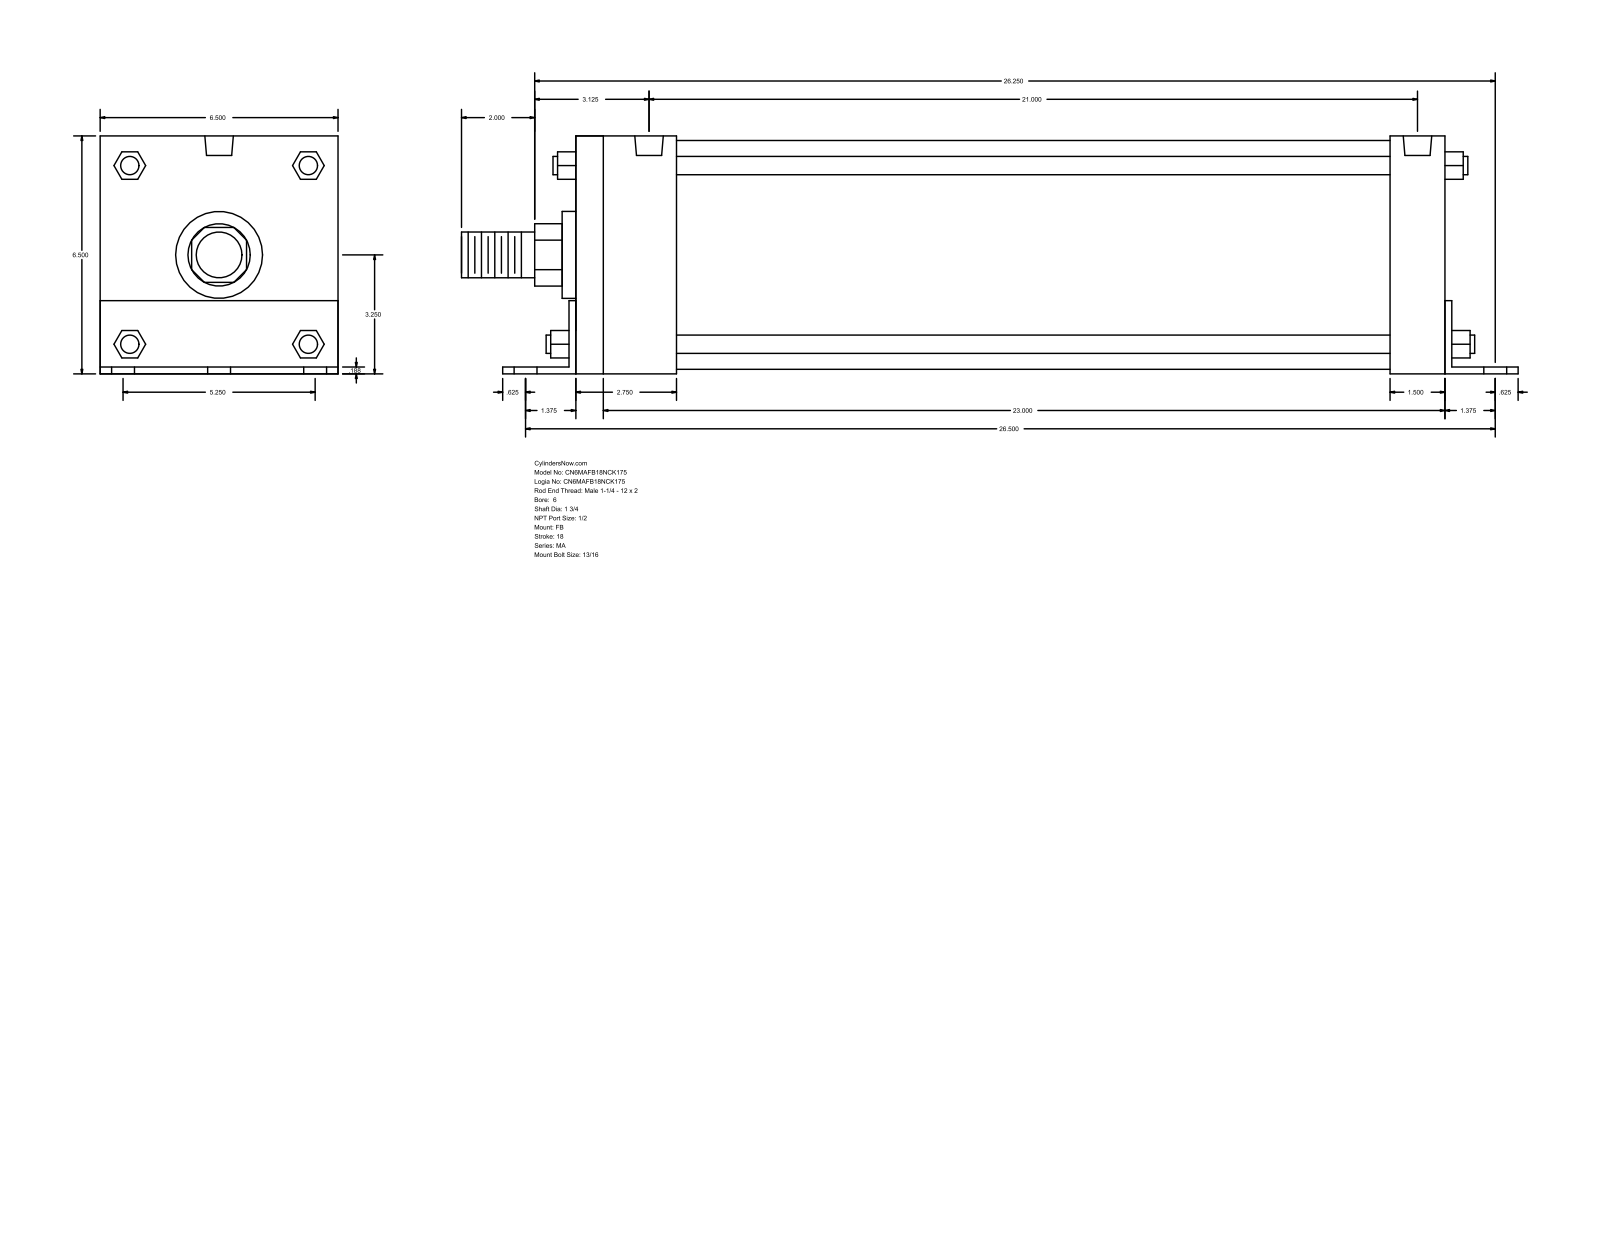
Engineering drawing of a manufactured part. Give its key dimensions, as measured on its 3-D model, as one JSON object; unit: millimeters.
{"part_name": "MA_FB__0600_1.75", "step_written_by": "GSSL Pune (CONFIG_CONTROL_DESIGN)", "units": "millimeters", "bodies": {"solids": 0, "faces": 140, "planar": 105, "cylindrical": 35, "other": 0}, "overall_size": [733.42, 165.15, 165.1], "round_holes": [[20.64, 6], [17.46, 4], [19.77, 2]], "round_bosses_or_shafts": [[12.7, 4], [158.75, 1], [60.33, 1], [44.45, 1], [31.75, 1]], "partial_cylinders_radius": [[21.63, 1], [32.05, 1]], "face_to_face_distances": [165.1, 4.76, 603.26, 165.15, 608.02, 4.71, 160.39, 612.78, 38.1, 69.85], "hole_center_spacings": [66.67, 676.39, 673.1, 85.78, 108.6, 133.34, 533.39, 591.14]}
